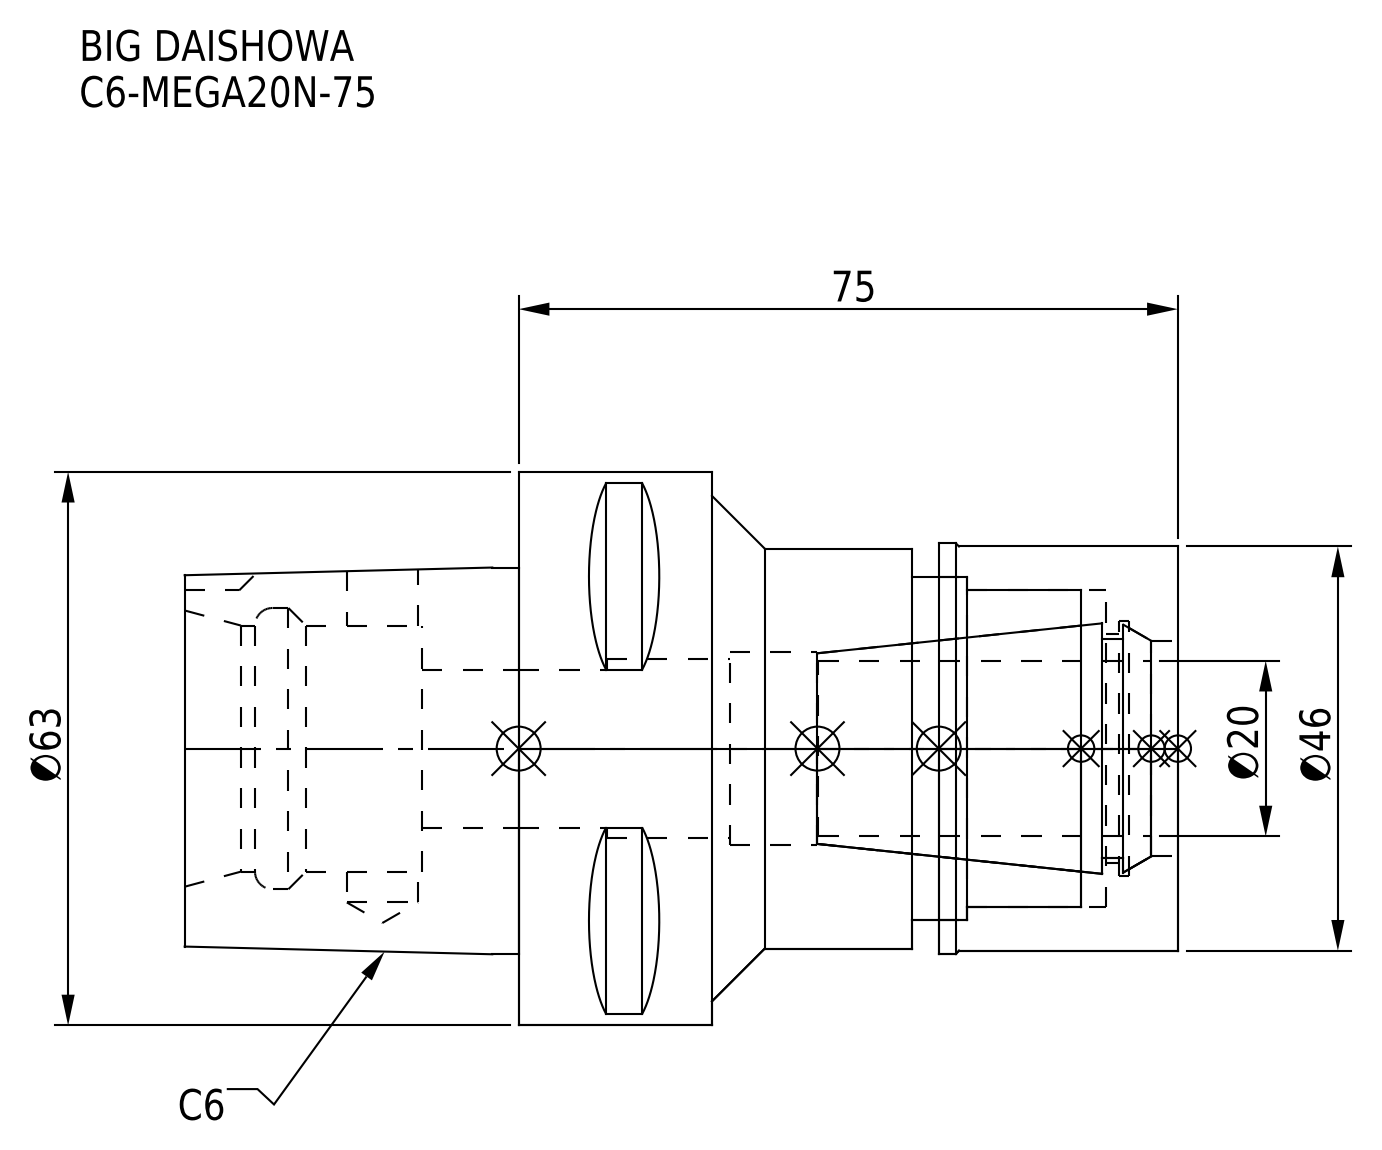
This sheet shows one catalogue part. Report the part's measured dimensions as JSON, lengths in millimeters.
{"part_name": "DXF_TEMP_ASSY_ASM_4_ASM.stp; C6-MEGA20N-75-200-FreeParts; C6-MEGA20N-75-200.stp; C6-MEGA20N-75-200_ASM.stp (+3 more)", "step_written_by": "SolidWorks 2019 (CONFIG_CONTROL_DESIGN)", "units": "millimeters", "bodies": {"solids": 2, "faces": 95, "planar": 38, "cylindrical": 39, "other": 18}, "overall_size": [113, 63, 63], "volume_mm3": 156719, "surface_area_mm2": 37448, "round_holes": [[8.1, 1], [18, 1], [20.3, 1], [22, 1], [24.5, 1], [26, 1], [28, 1], [29, 1], [32, 1], [36, 1], [39, 1]], "round_bosses_or_shafts": [[63, 1], [46.7, 1], [46, 1], [45.5, 1]], "partial_cylinders_radius": [[5, 1]], "face_to_face_distances": [75, 22, 44.8, 11, 53, 27.2, 25.8, 47.8, 113, 85.8]}
